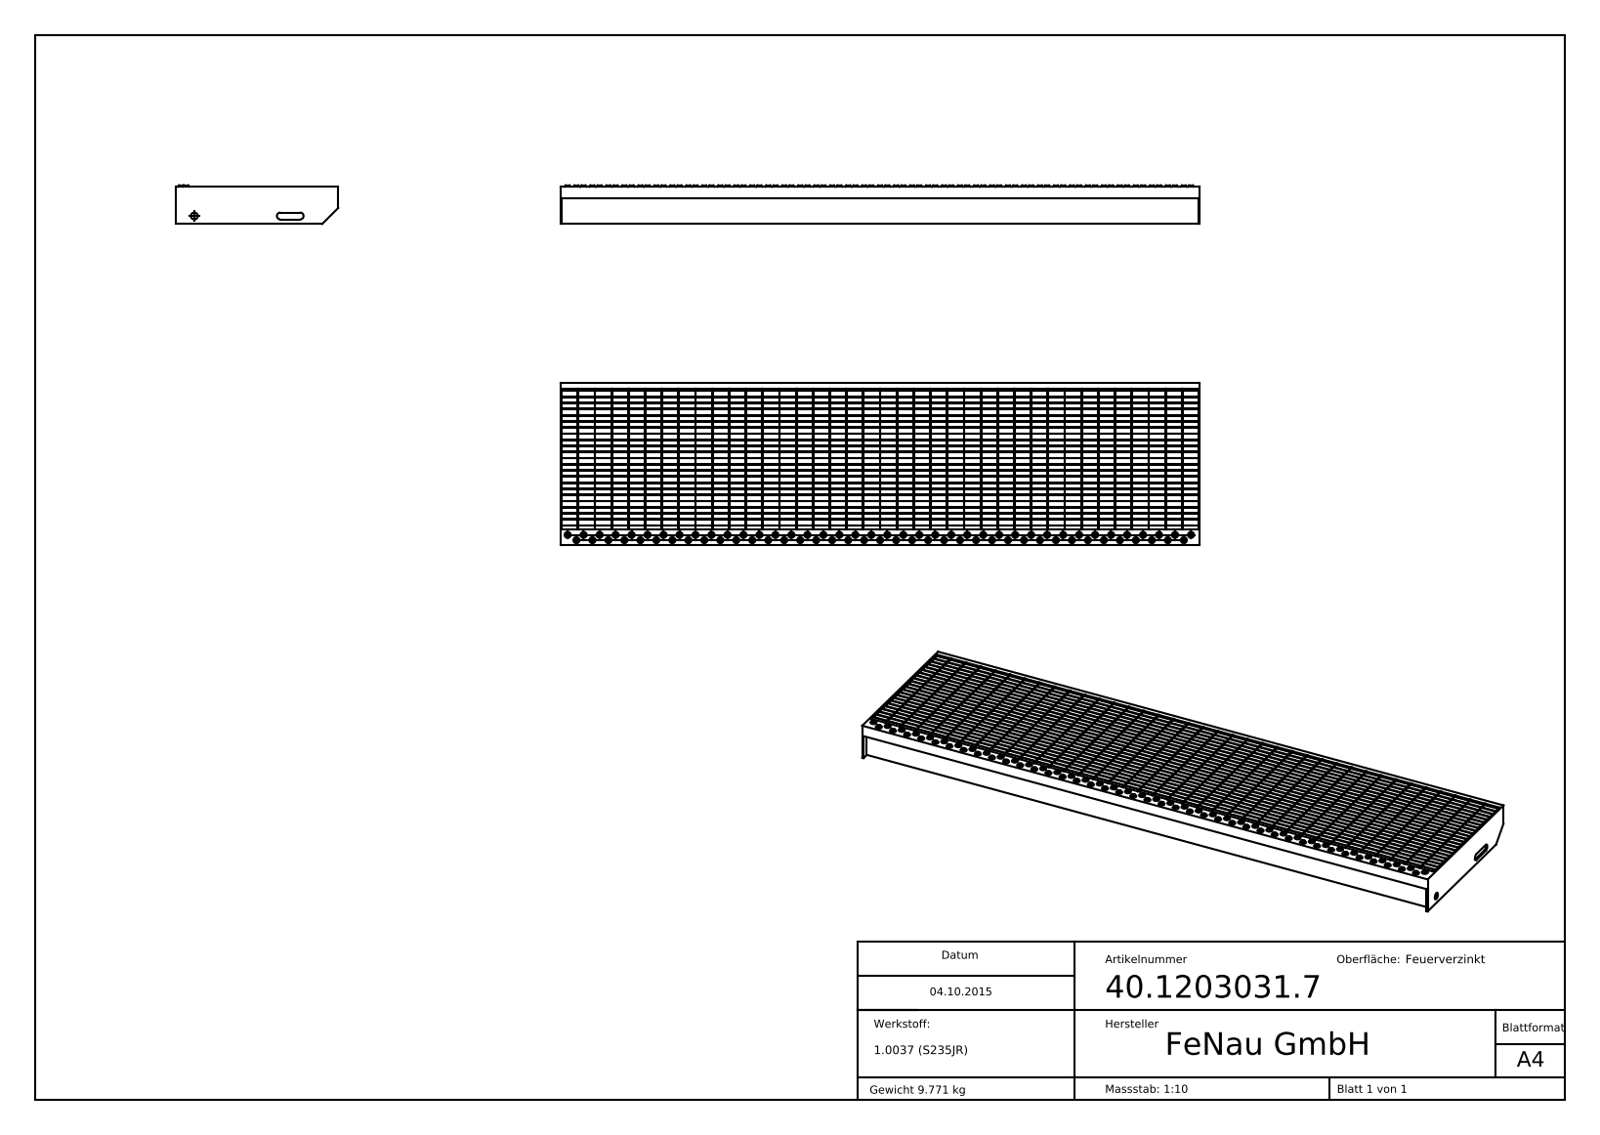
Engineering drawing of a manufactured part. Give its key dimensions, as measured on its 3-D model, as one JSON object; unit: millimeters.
{"part_name": "40.1203031.7", "step_written_by": "SolidWorks 2015 (CONFIG_CONTROL_DESIGN)", "units": "millimeters", "bodies": {"solids": 52, "faces": 1154, "planar": 734, "cylindrical": 168, "other": 252}, "overall_size": [1200, 305, 72.67], "volume_mm3": 1253000, "surface_area_mm2": 1567000, "round_holes": [[7, 79], [13, 1]], "partial_cylinders_radius": [[6.5, 2]], "face_to_face_distances": [2, 1.5, 13, 11.5, 31.5, 23, 63, 33, 20, 281.5], "hole_center_spacings": [30, 60, 90, 120, 150, 180, 210, 240]}
